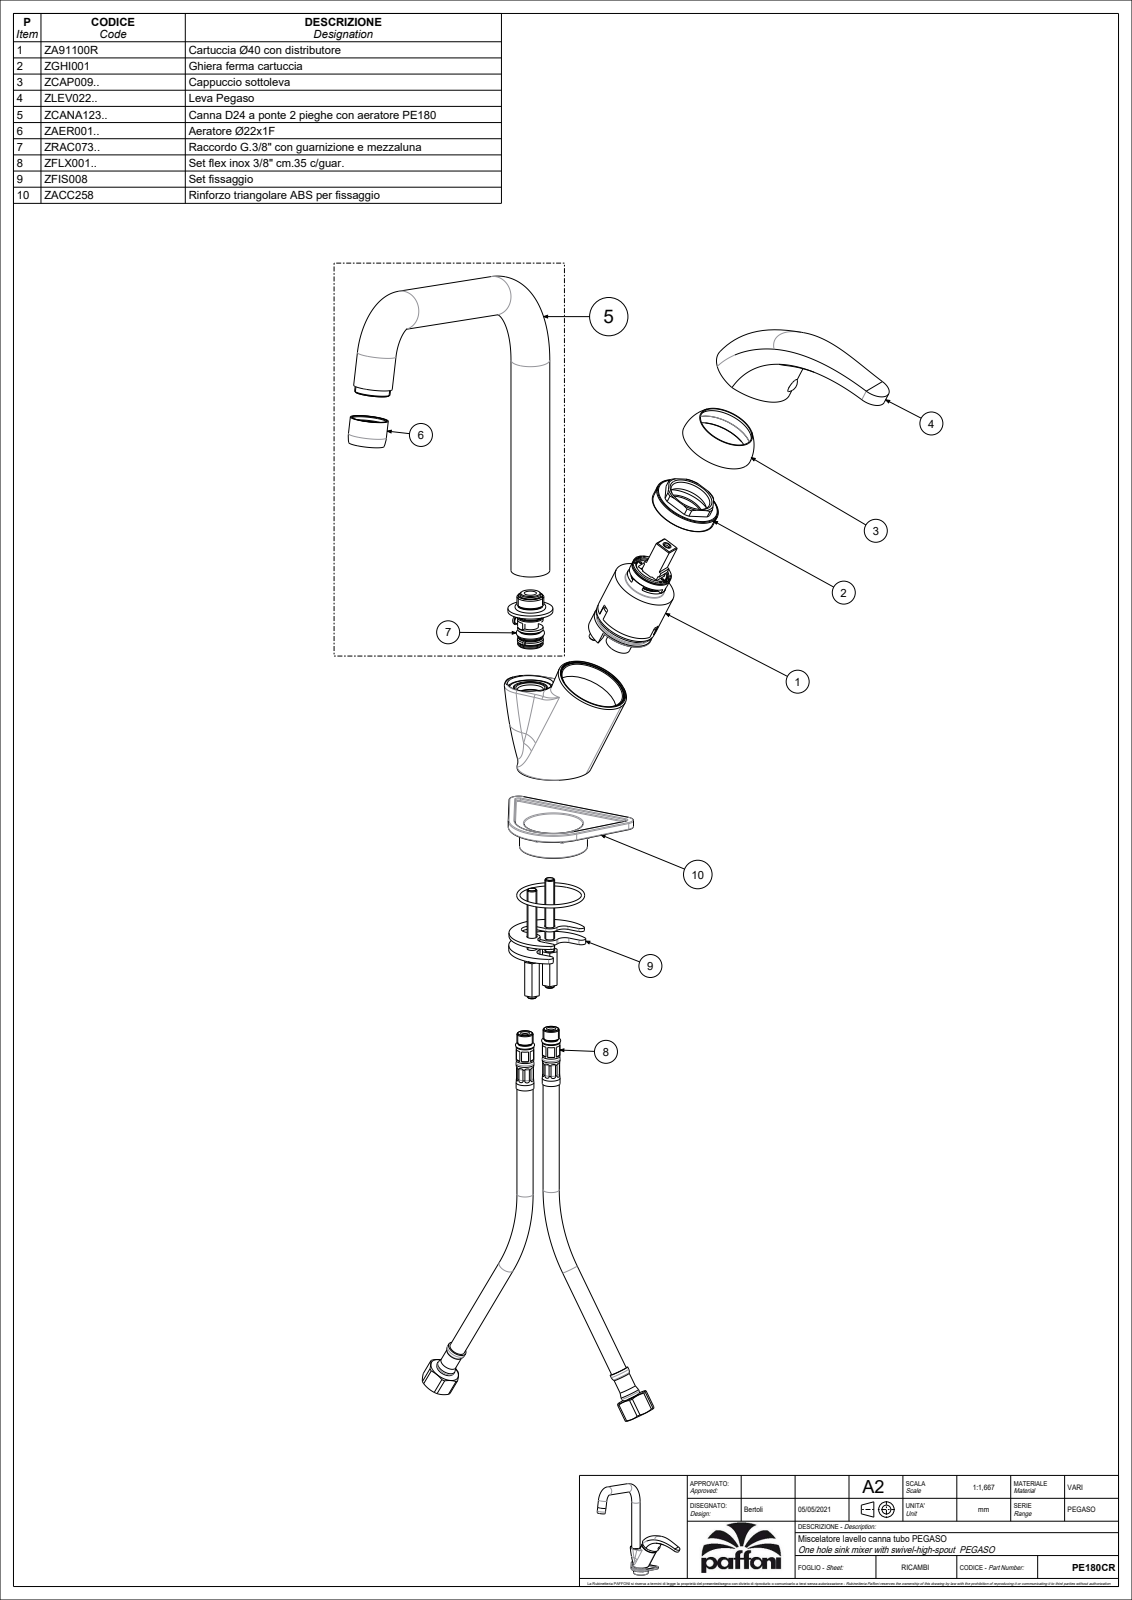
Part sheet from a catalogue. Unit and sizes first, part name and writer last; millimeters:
Units: millimetres
Overall size (bounding box): 285.82 × 234.73 × 159.43
Round holes (diameter × count): ⌀21 ×4, ⌀5.5 ×3, ⌀8 ×3, ⌀6 ×2, ⌀9 ×2, ⌀11 ×2, ⌀16 ×2, ⌀17 ×2, ⌀4 ×1, ⌀7.5 ×1, ⌀8.5 ×1, ⌀14.1 ×1
Round bosses / shafts (diameter × count): ⌀24 ×3, ⌀27.8 ×1, ⌀23.6 ×1, ⌀20.8 ×1, ⌀20 ×1, ⌀19.5 ×1, ⌀18.8 ×1, ⌀16.8 ×1
Partial cylindrical surfaces — rounded edges, fillets, slot ends (radius × count): R1 ×8, R3.9 ×1, R15.5 ×1
Main face-to-face distances: 46.5, 14.5, 61, 2, 0.5, 1, 84.22, 37.72, 23.22, 1.5
Hole centre spacings: 8.6, 15.62, 15.81, 21.83, 24.2, 14, 15, 24
Volume: 165 221 mm³ · Surface area: 110 235 mm²
Bodies: 3 solids, 1911 faces (1651 planar, 128 cylindrical, 132 other)
Part name (STEP PRODUCT): PE180CR_SW0001
STEP written by: CREO PARAMETRIC BY PTC INC, 2022124 (CONFIG_CONTROL_DESIGN)
